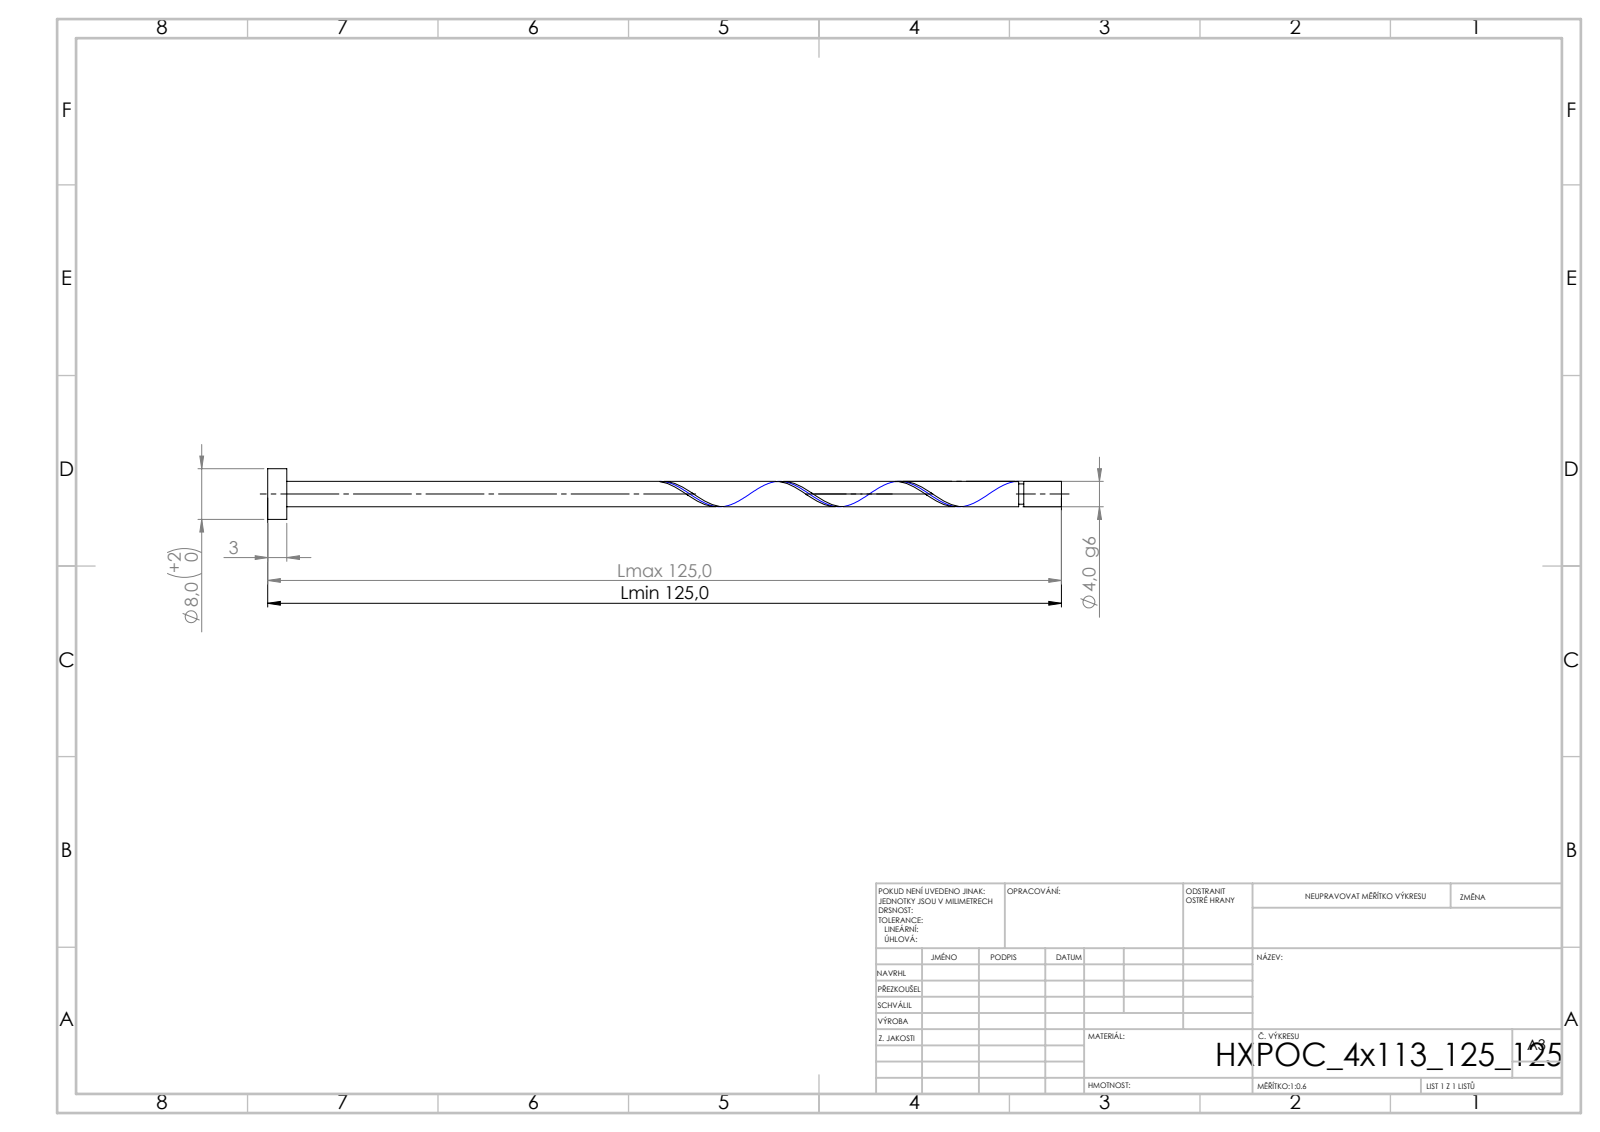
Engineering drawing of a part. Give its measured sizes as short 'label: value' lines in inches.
written by: SolidWorks 2019 (CONFIG_CONTROL_DESIGN)
unit: in
bodies: 1 solid, 21 faces (6 planar, 14 cylindrical, 1 other)
size: 4.921 × 0.315 × 0.315
volume: 0.102 in³; area: 2.703 in²
bosses: 1× ⌀0.315, 1× ⌀0.157, 1× ⌀0.126
face distances: 0.118, 4.921, 4.803, 4.688, 4.57, 0.233, 4.657, 4.539, 0.031, 0.265
